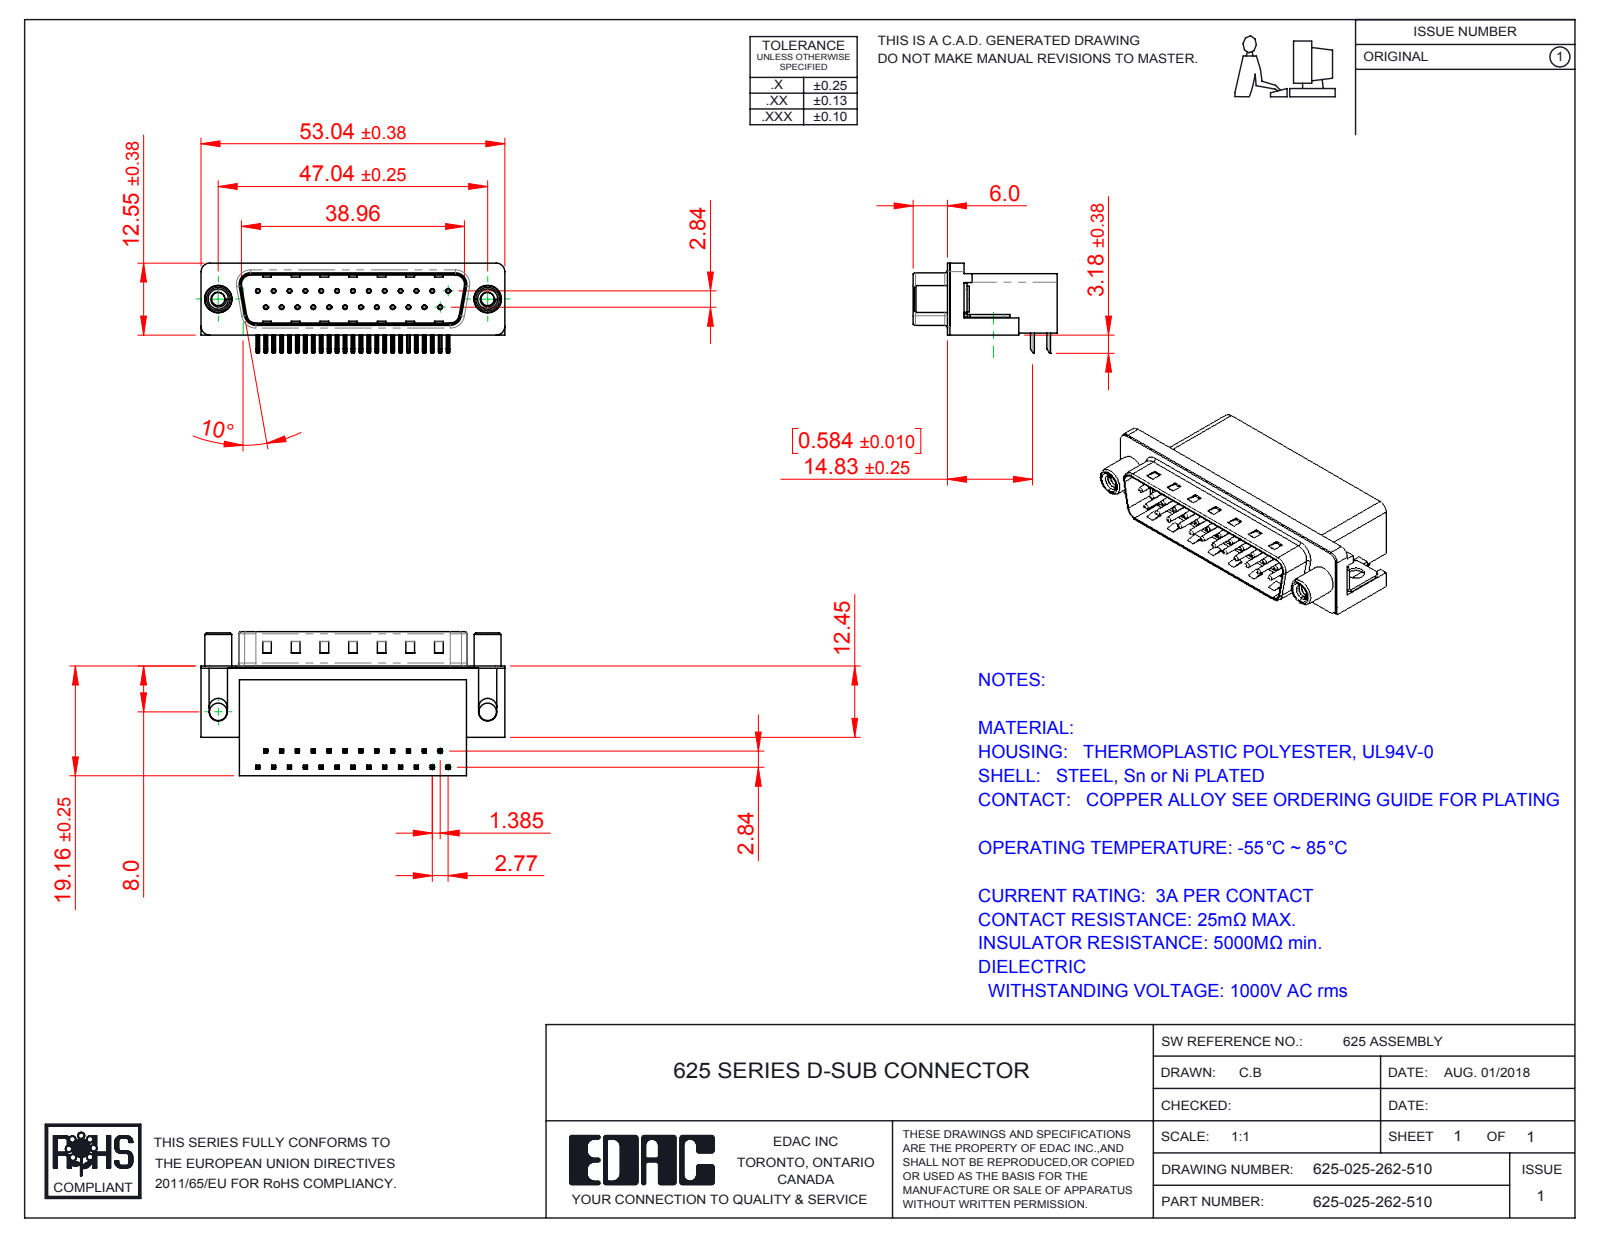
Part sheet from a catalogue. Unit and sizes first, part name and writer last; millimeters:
Units: millimetres
Overall size (bounding box): 53.04 × 25.16 × 15.73
Round holes (diameter × count): ⌀0.35 ×25, ⌀0.8 ×25, ⌀2.3 ×2, ⌀3.05 ×2, ⌀3.1 ×2, ⌀4 ×2, ⌀4.8 ×2, ⌀5 ×2
Round bosses / shafts (diameter × count): ⌀0.75 ×25, ⌀4.9 ×2, ⌀4.7 ×2, ⌀4.5 ×2, ⌀3.85 ×2
Partial cylindrical surfaces — rounded edges, fillets, slot ends (radius × count): R0.25 ×100, R0.12 ×50, R1 ×16, R0.5 ×9, R1.6 ×8, R1.5 ×7, R0.9 ×4, R2 ×4
Main face-to-face distances: 0.4, 10.35, 18.76, 2.1, 8.76, 10.46, 10.86, 1.7, 19.16, 2.9
Hole centre spacings: 3.16, 2.77, 11.08, 5.54, 8.31, 5.03, 13.85, 7.48
Volume: 9 252 mm³ · Surface area: 9 048 mm²
Bodies: 31 solids, 2259 faces (1397 planar, 669 cylindrical, 193 other)
Part name (STEP PRODUCT): 625 Round Threaded Standoff; 625 Contact Bottom; 625-025-262-510; 625 Thru Hole Board Mount (+3 more)
STEP written by: SolidWorks 2016 (CONFIG_CONTROL_DESIGN)
